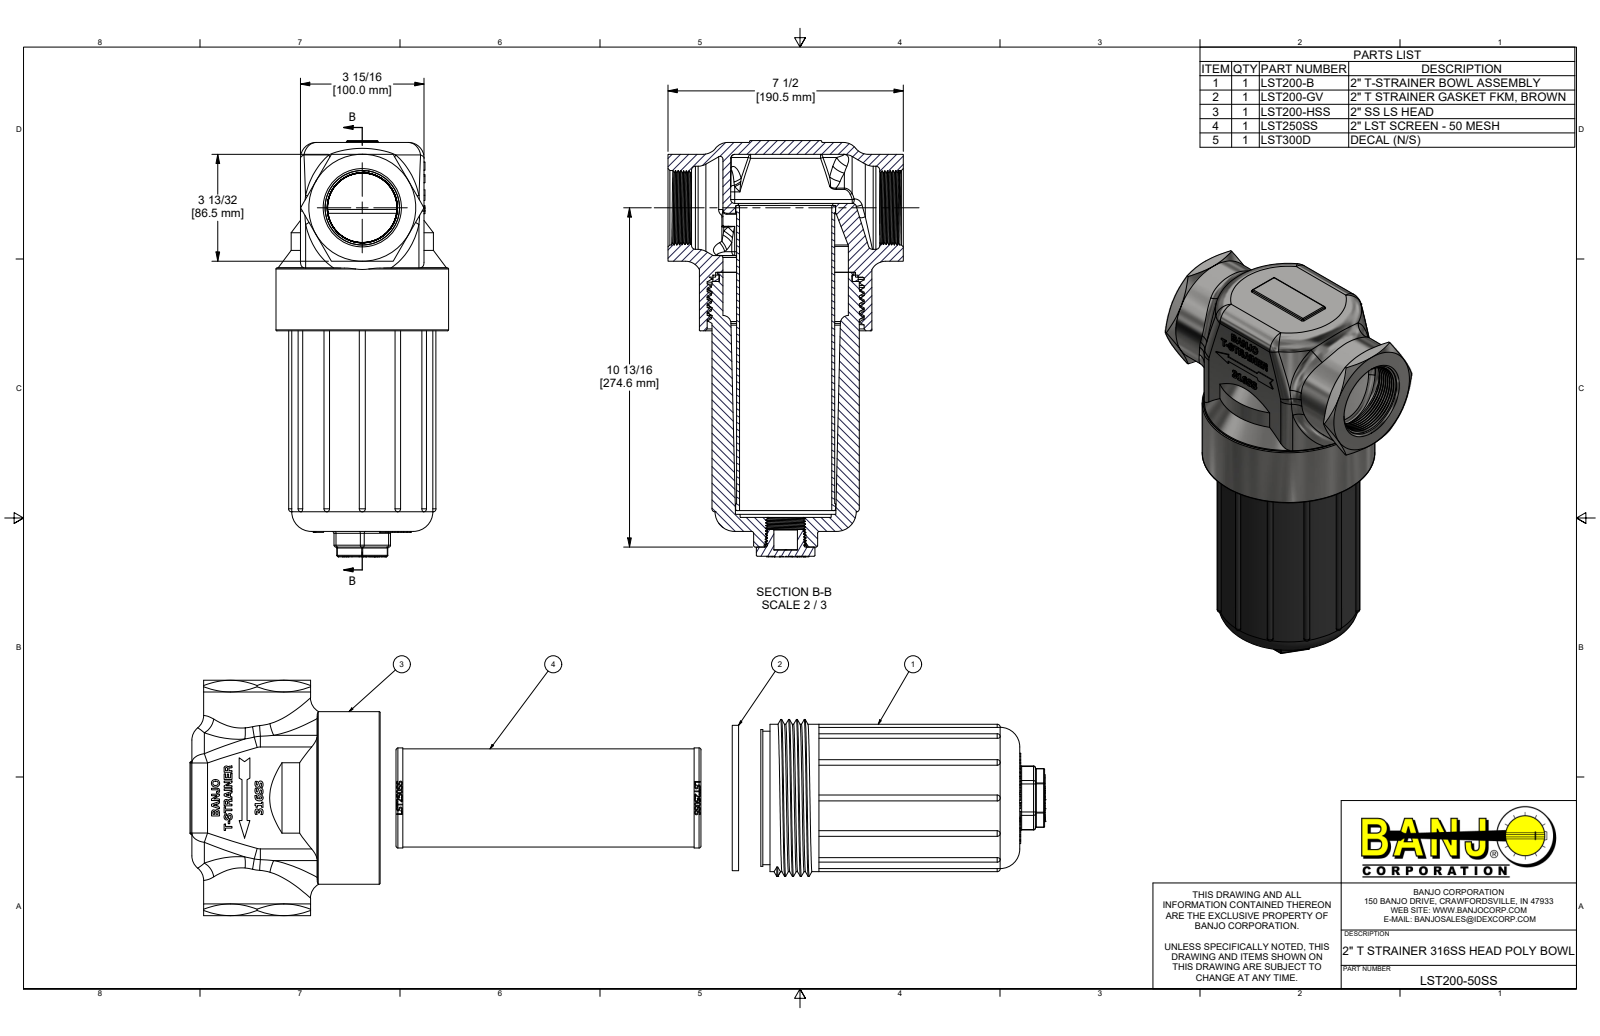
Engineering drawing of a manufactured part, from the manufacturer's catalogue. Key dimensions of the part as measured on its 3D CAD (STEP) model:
Part name (STEP PRODUCT): LST200-50SS; LST200-HSS; LST200B; LST200XB (+4 more)
STEP written by: Autodesk Inventor 2019 (AUTOMOTIVE_DESIGN)
Units: inches
Bodies: 6 solids, 1925 faces (793 planar, 180 cylindrical, 952 other)
Overall size (bounding box): 21.417 × 7.5 × 5.5
Volume: 110.3 in³ · Surface area: 950.7 in²
Round holes (diameter × count): ⌀0.75 ×1, ⌀2.646 ×1, ⌀2.9 ×1, ⌀2.937 ×1, ⌀3 ×1, ⌀3.18 ×1, ⌀3.2 ×1, ⌀4 ×1, ⌀4.225 ×1, ⌀4.458 ×1, ⌀4.729 ×1, ⌀5 ×1
Round bosses / shafts (diameter × count): ⌀5.5 ×1, ⌀4.693 ×1, ⌀4.631 ×1, ⌀4.5 ×1, ⌀4.36 ×1, ⌀4.25 ×1, ⌀3.406 ×1, ⌀3.188 ×1
Partial cylindrical surfaces — rounded edges, fillets, slot ends (radius × count): R0.03 ×28, R0.094 ×21, R0.125 ×21, R0.06 ×12, R0.5 ×8, R0.09 ×2, R0.12 ×2, R0.391 ×1
Main face-to-face distances: 0.38, 3.557, 0.38, 3.938, 4.047, 4.427, 7.515, 11.562, 11.942, 0.29
